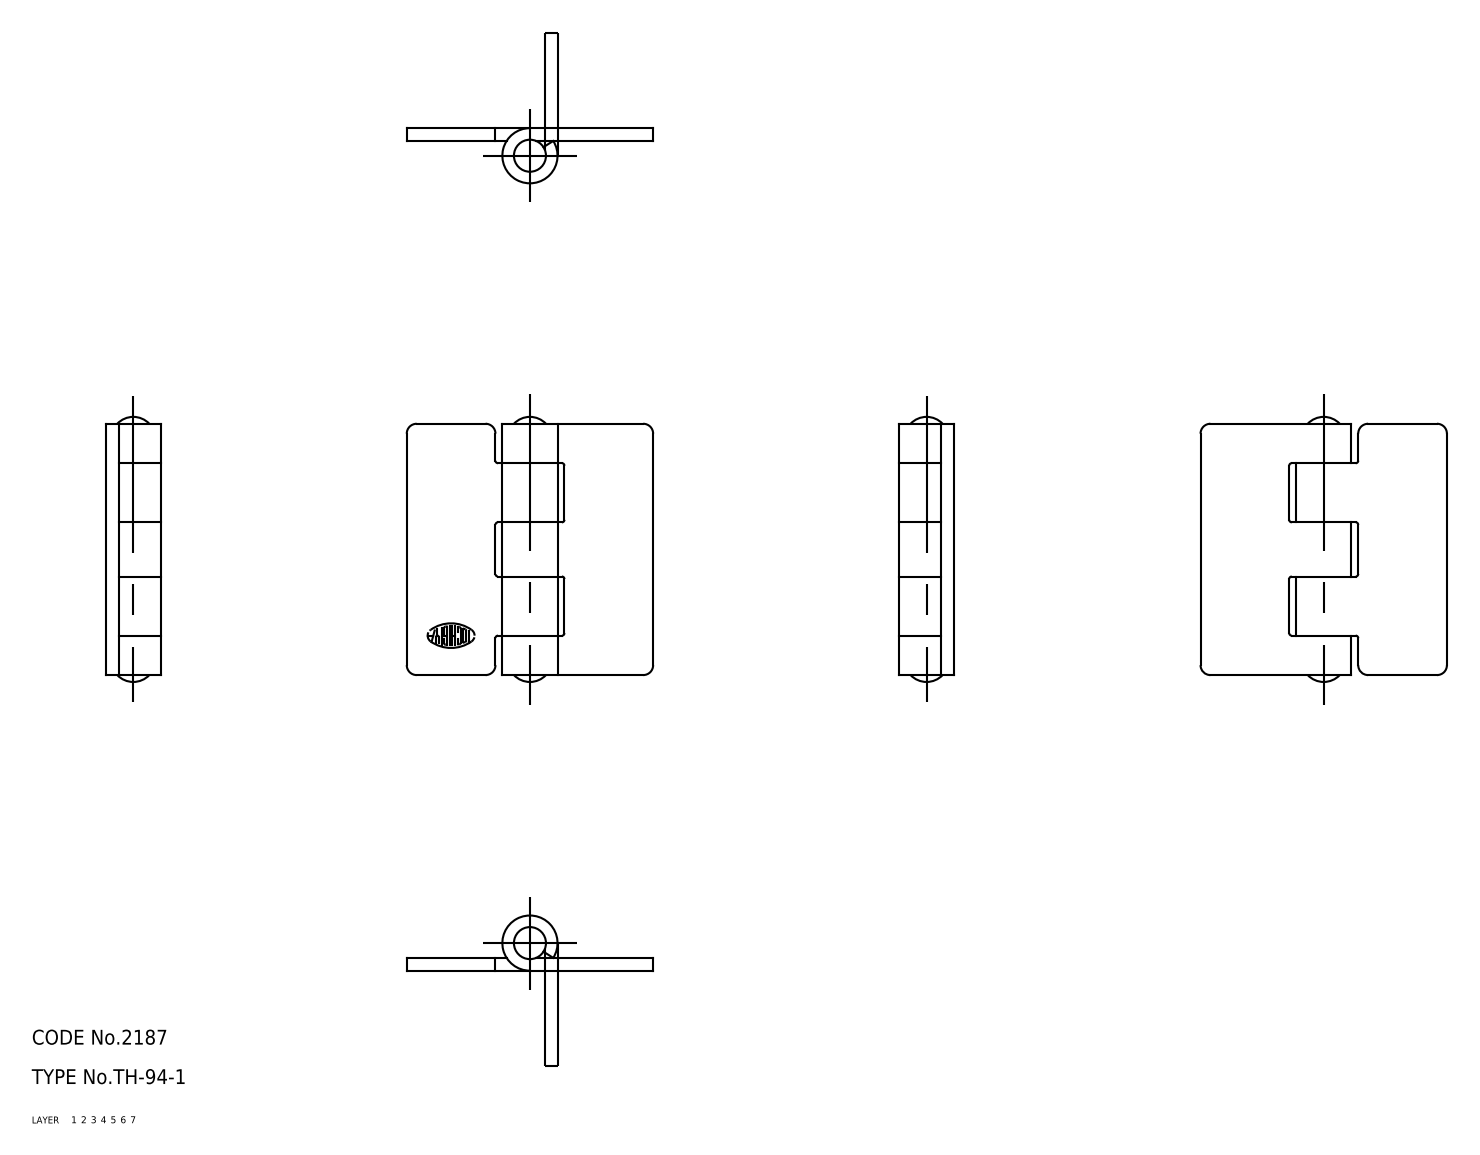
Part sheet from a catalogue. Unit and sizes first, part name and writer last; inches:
Units: inches
Overall size (bounding box): 2.118 × 1.969 × 0.441
Volume: 0.622 in³ · Surface area: 14.28 in²
Bodies: 3 solids, 58 faces (0 planar, 0 cylindrical, 58 other)
Part name (STEP PRODUCT): 67111878; 67111891; 67111904
STEP written by: CADfix (AUTOMOTIVE_DESIGN)
